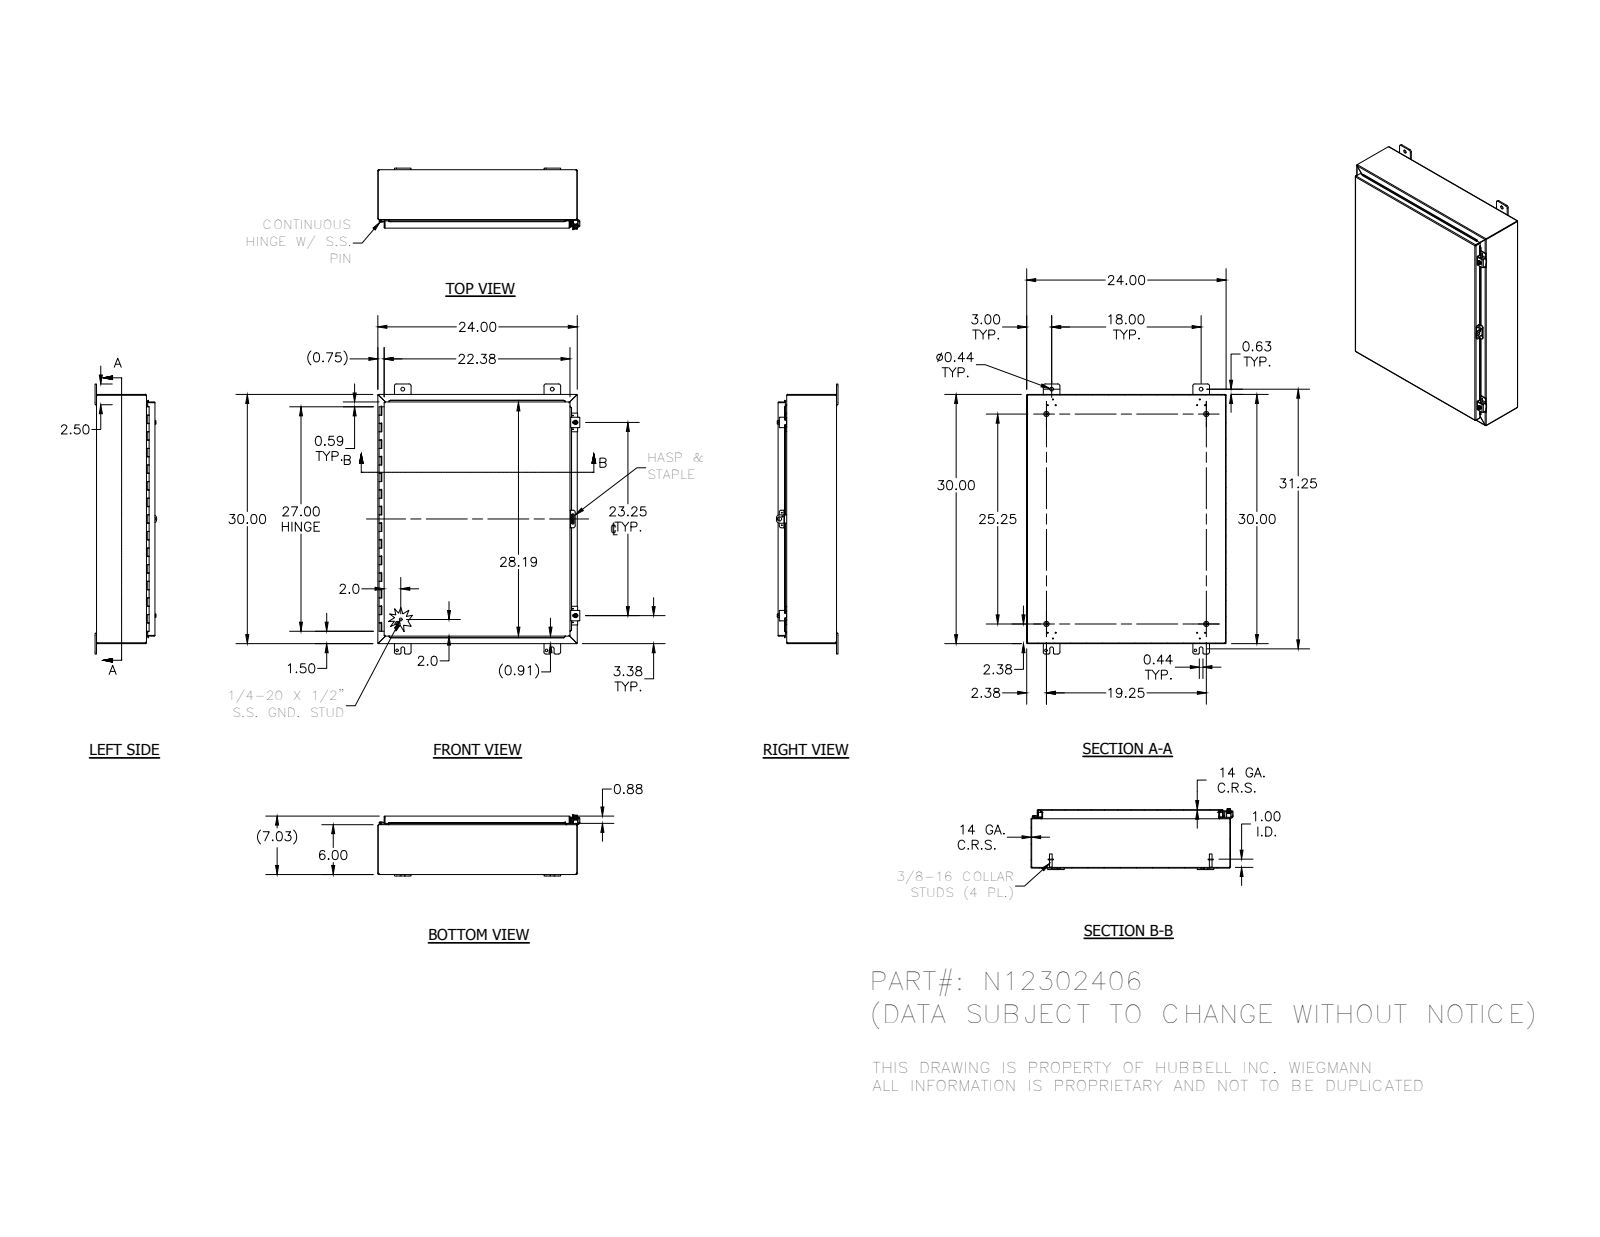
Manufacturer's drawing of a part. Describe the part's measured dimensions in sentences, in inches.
The part is named "N12302406; 34840; 38420; N12302406BKP (+8 more)". Its 3-D file was written by "Autodesk Inventor 2012 (AUTOMOTIVE_DESIGN)". It is 27 solids with 1033 faces: 566 planar, 350 cylindrical and 117 other. Overall it measures 32.5 by 24.311 by 7.41 inches. Its volume is 190.1 cubic inches and its surface area 4 969 square inches. Round holes: 12 of diameter 0.12, 7 of diameter 0.11, 4 of diameter 0.313, 4 of diameter 0.438, 2 of diameter 0.211, 2 of diameter 0.281, 2 of diameter 0.3, 1 of diameter 0.125, 1 of diameter 0.156, 1 of diameter 0.5. Round bosses or shafts: 4 of diameter 0.625, 4 of diameter 0.33, 4 of diameter 0.25, 2 of diameter 0.52, 2 of diameter 0.5, 2 of diameter 0.35, 2 of diameter 0.115, 1 of diameter 0.337. Partial cylindrical surfaces (rounded edges, fillets, slot ends): 27 of radius 0.03, 25 of radius 0.063, 25 of radius 0.125, 25 of radius 0.25, 23 of radius 0.031, 23 of radius 0.105, 8 of radius 0.07, 4 of radius 0.1. The main face-to-face distances are 0.074, 6.959, 6.885, 7.033, 23.926, 29.926, 5.926, 1.033, 23.852, 24. The hole center spacings are 18, 0.759, 0.94, 0.969, 1.995, 17.37, 18.339, 27.38.
